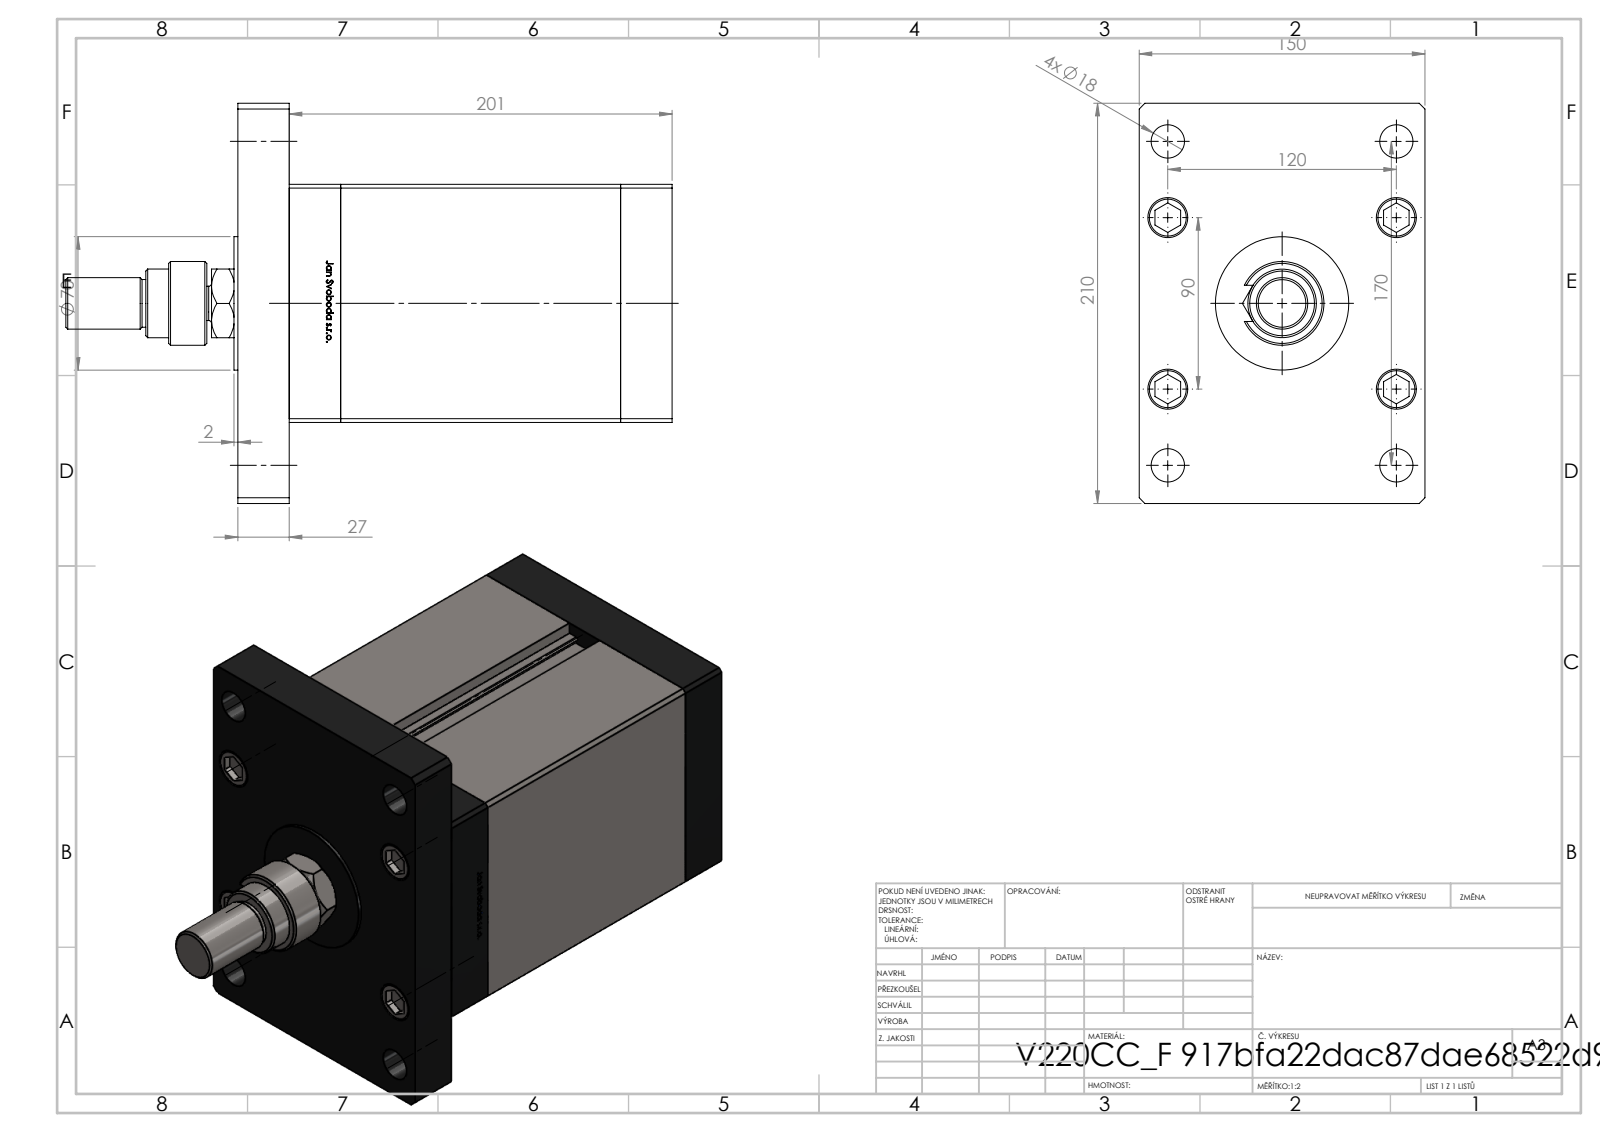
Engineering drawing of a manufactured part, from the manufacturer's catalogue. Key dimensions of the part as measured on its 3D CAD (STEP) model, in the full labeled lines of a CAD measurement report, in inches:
Part name (STEP PRODUCT): V220C_F; MFA; V220C_F_MIDDLE; V220C_VC_F (+4 more)
STEP written by: SolidWorks 2019 (CONFIG_CONTROL_DESIGN)
Units: inches
Bodies: 21 solids, 1395 faces (545 planar, 200 cylindrical, 650 other)
Overall size (bounding box): 12.531 × 8.268 × 5.906
Volume: 249.6 in³ · Surface area: 723.9 in²
Round holes (diameter × count): ⌀0.689 ×9, ⌀0.866 ×5, ⌀0.63 ×4, ⌀0.827 ×4, ⌀0.079 ×2, ⌀0.518 ×2, ⌀1.004 ×1, ⌀1.417 ×1, ⌀1.476 ×1
Round bosses / shafts (diameter × count): ⌀0.315 ×9, ⌀0.827 ×5, ⌀3.15 ×1, ⌀2.756 ×1, ⌀1.732 ×1, ⌀1.102 ×1, ⌀1.063 ×1, ⌀0.984 ×1
Partial cylindrical surfaces — rounded edges, fillets, slot ends (radius × count): R0.037 ×2, R0.374 ×1, R0.591 ×1, R0.689 ×1
Main face-to-face distances: 1.063, 6.85, 7.913, 5.906, 4.921, 5.787, 2.126, 8.976, 1.37, 0.307
Hole centre spacings: 2.008, 1.575, 2.953, 4.096, 4.724, 4.98, 5.118, 6.965
